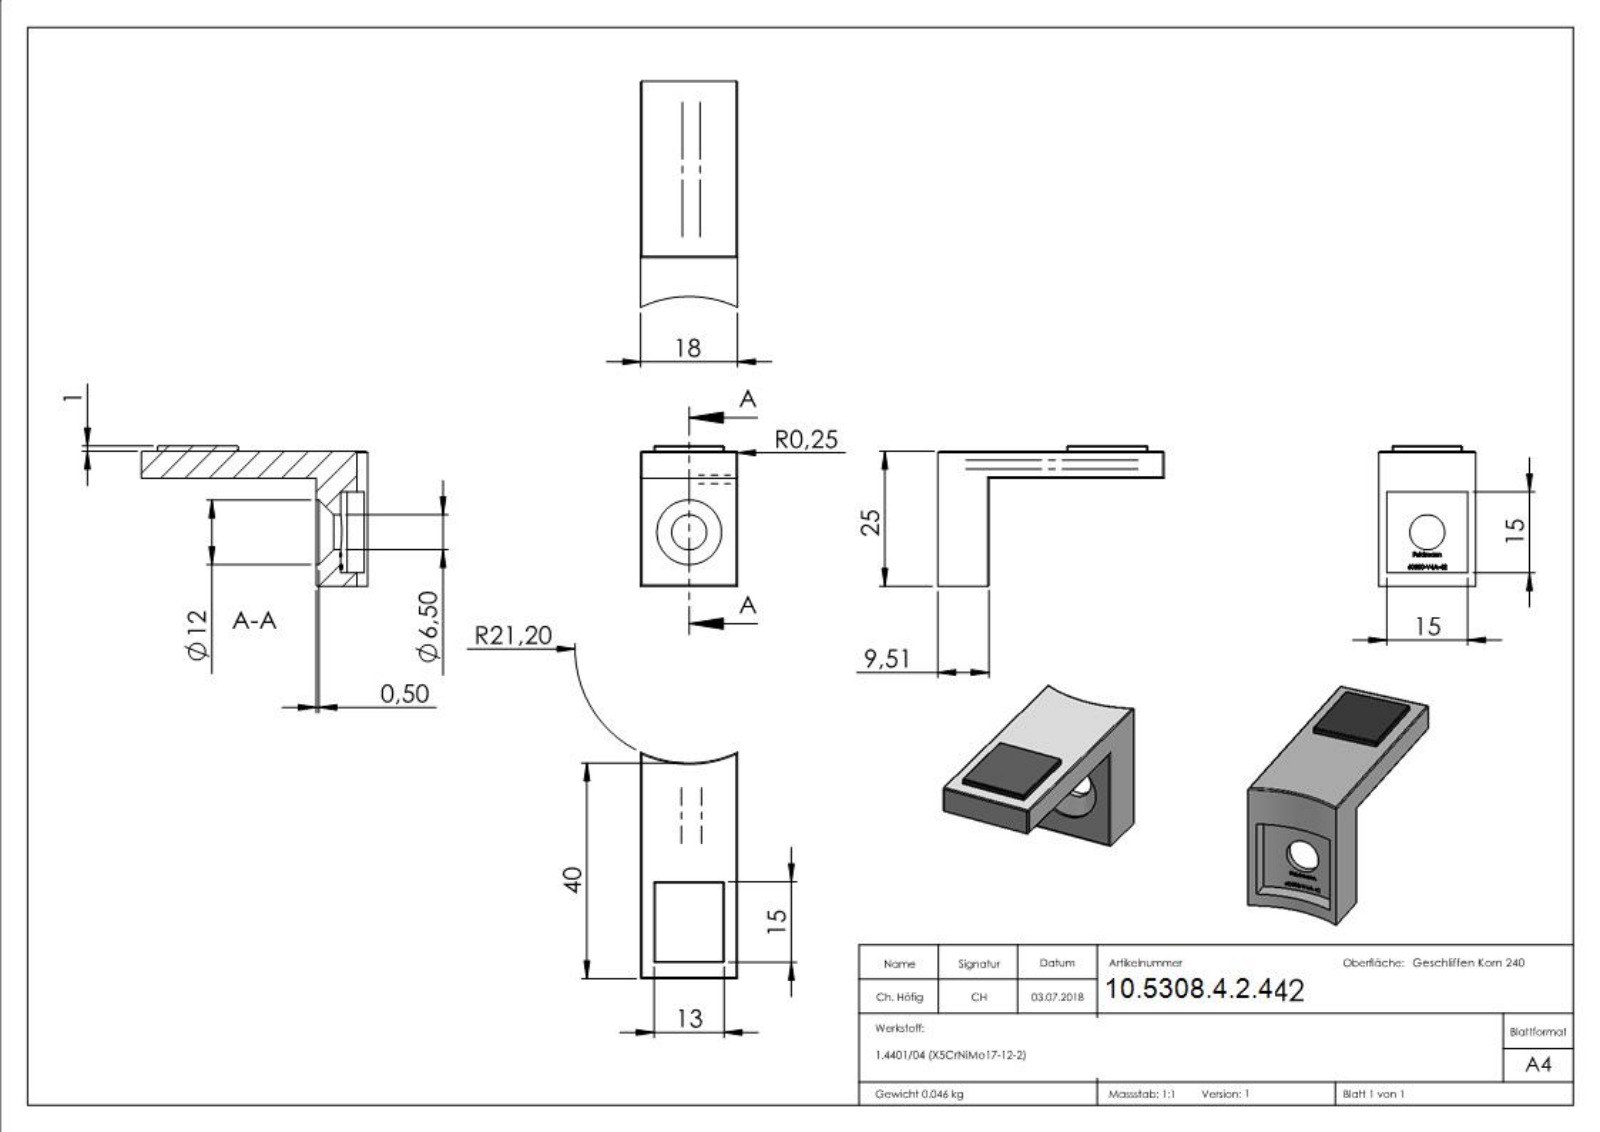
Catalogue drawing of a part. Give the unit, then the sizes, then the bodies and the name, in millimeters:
Units: millimetres
Overall size (bounding box): 42.01 × 26 × 18
Round holes (diameter × count): ⌀6.5 ×1, ⌀12 ×1
Partial cylindrical surfaces — rounded edges, fillets, slot ends (radius × count): R0.25 ×10, R0.2 ×8, R21.2 ×1, R24.2 ×1, R24.3 ×1
Main face-to-face distances: 5, 18, 1, 6, 20, 25, 26, 2.5, 15, 1.5
Volume: 5 808 mm³ · Surface area: 3 798 mm²
Bodies: 2 solids, 308 faces (123 planar, 57 cylindrical, 128 other)
Part name (STEP PRODUCT): 60500-V4A-42
STEP written by: SolidWorks 2015 (CONFIG_CONTROL_DESIGN)
